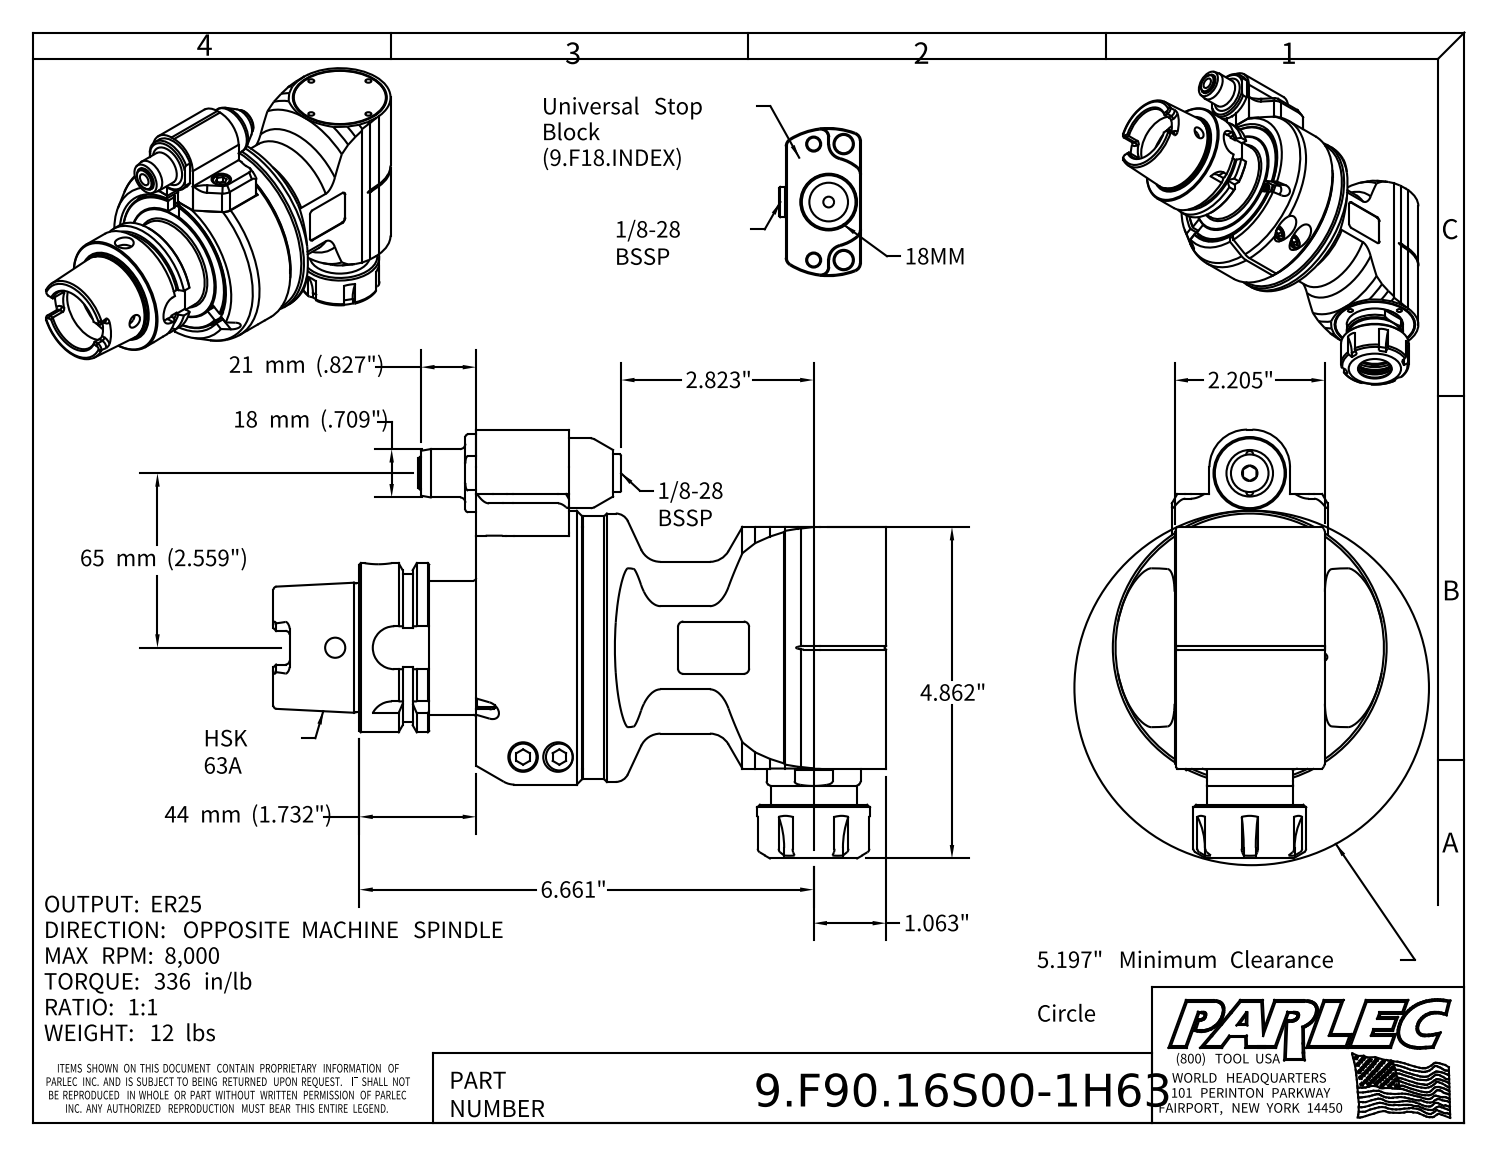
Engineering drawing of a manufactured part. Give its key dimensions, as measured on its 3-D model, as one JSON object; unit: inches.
{"part_name": "9.F90.16S00-1H63; 9_F90_16S00; 9_GA1_566_2_1_H63; 9FL1ATC (+4 more)", "step_written_by": "Autodesk Inventor 2022 (AUTOMOTIVE_DESIGN)", "units": "inches", "bodies": {"solids": 5, "faces": 578, "planar": 271, "cylindrical": 140, "other": 167}, "overall_size": [8.984, 6.289, 4.016], "volume_in3": 60.53, "surface_area_in2": 228.1, "round_holes": [[0.126, 4], [0.102, 2], [0.165, 2], [0.197, 2], [0.409, 2], [0.433, 2], [0.492, 2], [1.063, 2], [0.098, 1], [0.118, 1], [0.256, 1], [0.276, 1]], "round_bosses_or_shafts": [[0.394, 4], [0.236, 4], [0.709, 2], [0.315, 2], [0.098, 2], [4.016, 1], [3.937, 1], [3.858, 1]], "partial_cylinders_radius": [[0.079, 12], [0.059, 6], [0.984, 6], [0.113, 4], [0.157, 4], [0.315, 4], [0.016, 2], [0.02, 2]], "face_to_face_distances": [1.26, 1.024, 0.02, 1.252, 0.039, 0.276, 1.555, 0.303, 0.295, 0.984], "hole_center_spacings": [0.846, 1.197, 0.276, 1.693, 6.442, 0.512, 0.551, 1.72]}
